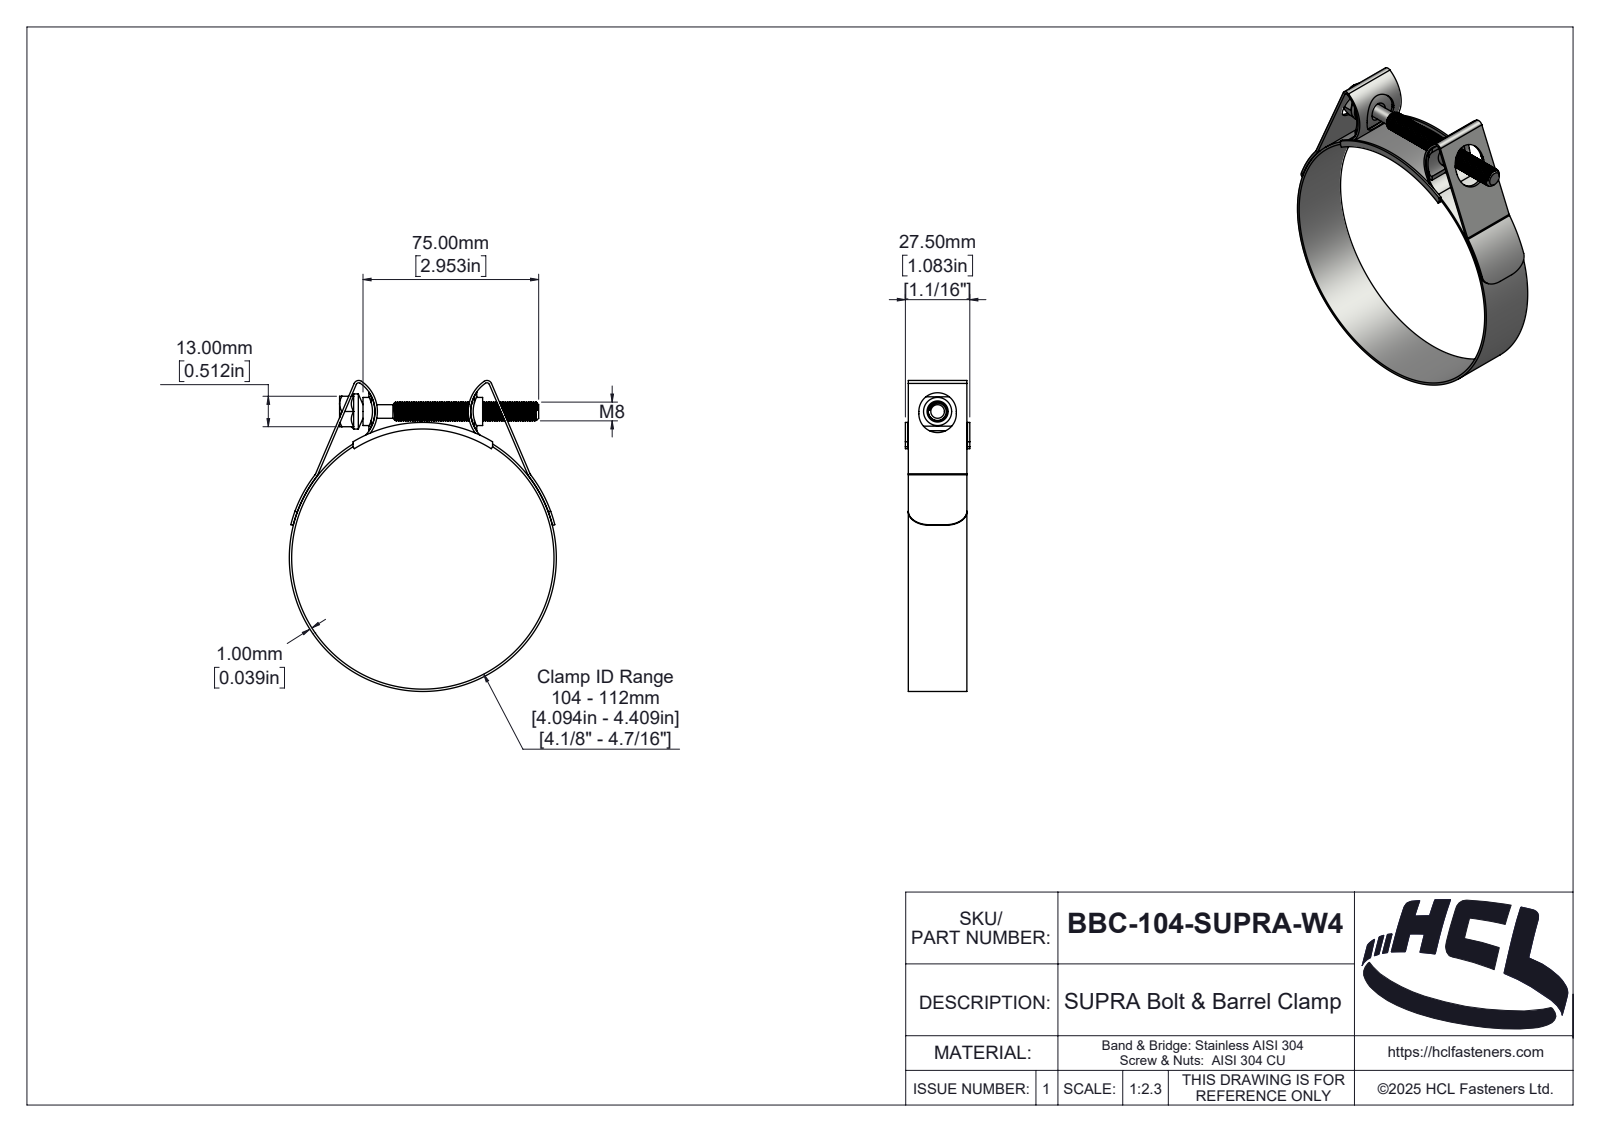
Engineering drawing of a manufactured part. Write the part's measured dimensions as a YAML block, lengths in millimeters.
part_name: "BBC-104-SUPRA-W4"
step_written_by: "SolidWorks 2025 (AUTOMOTIVE_DESIGN)"
units: millimeters
bodies: {solids: 5, faces: 365, planar: 46, cylindrical: 233, other: 86}
overall_size: [132.71, 114, 27.5]
volume: 18977
surface_area: 33521
round_holes:
  - {diameter: 112, count: 1}
round_bosses_or_shafts:
  - {diameter: 114, count: 1}
  - {diameter: 15.01, count: 1}
  - {diameter: 12, count: 1}
  - {diameter: 8, count: 1}
  - {diameter: 5.8, count: 1}
partial_cylinders:
  - {radius: 1, count: 4}
  - {radius: 1.1, count: 2}
  - {radius: 2, count: 2}
  - {radius: 2.1, count: 2}
  - {radius: 3, count: 2}
  - {radius: 8, count: 2}
  - {radius: 13.51, count: 2}
  - {radius: 14.51, count: 2}
face_to_face_distances: [1, 25, 1.25, 26.25, 26.5, 25.25, 27.5, 25.5, 13, 2.5]
